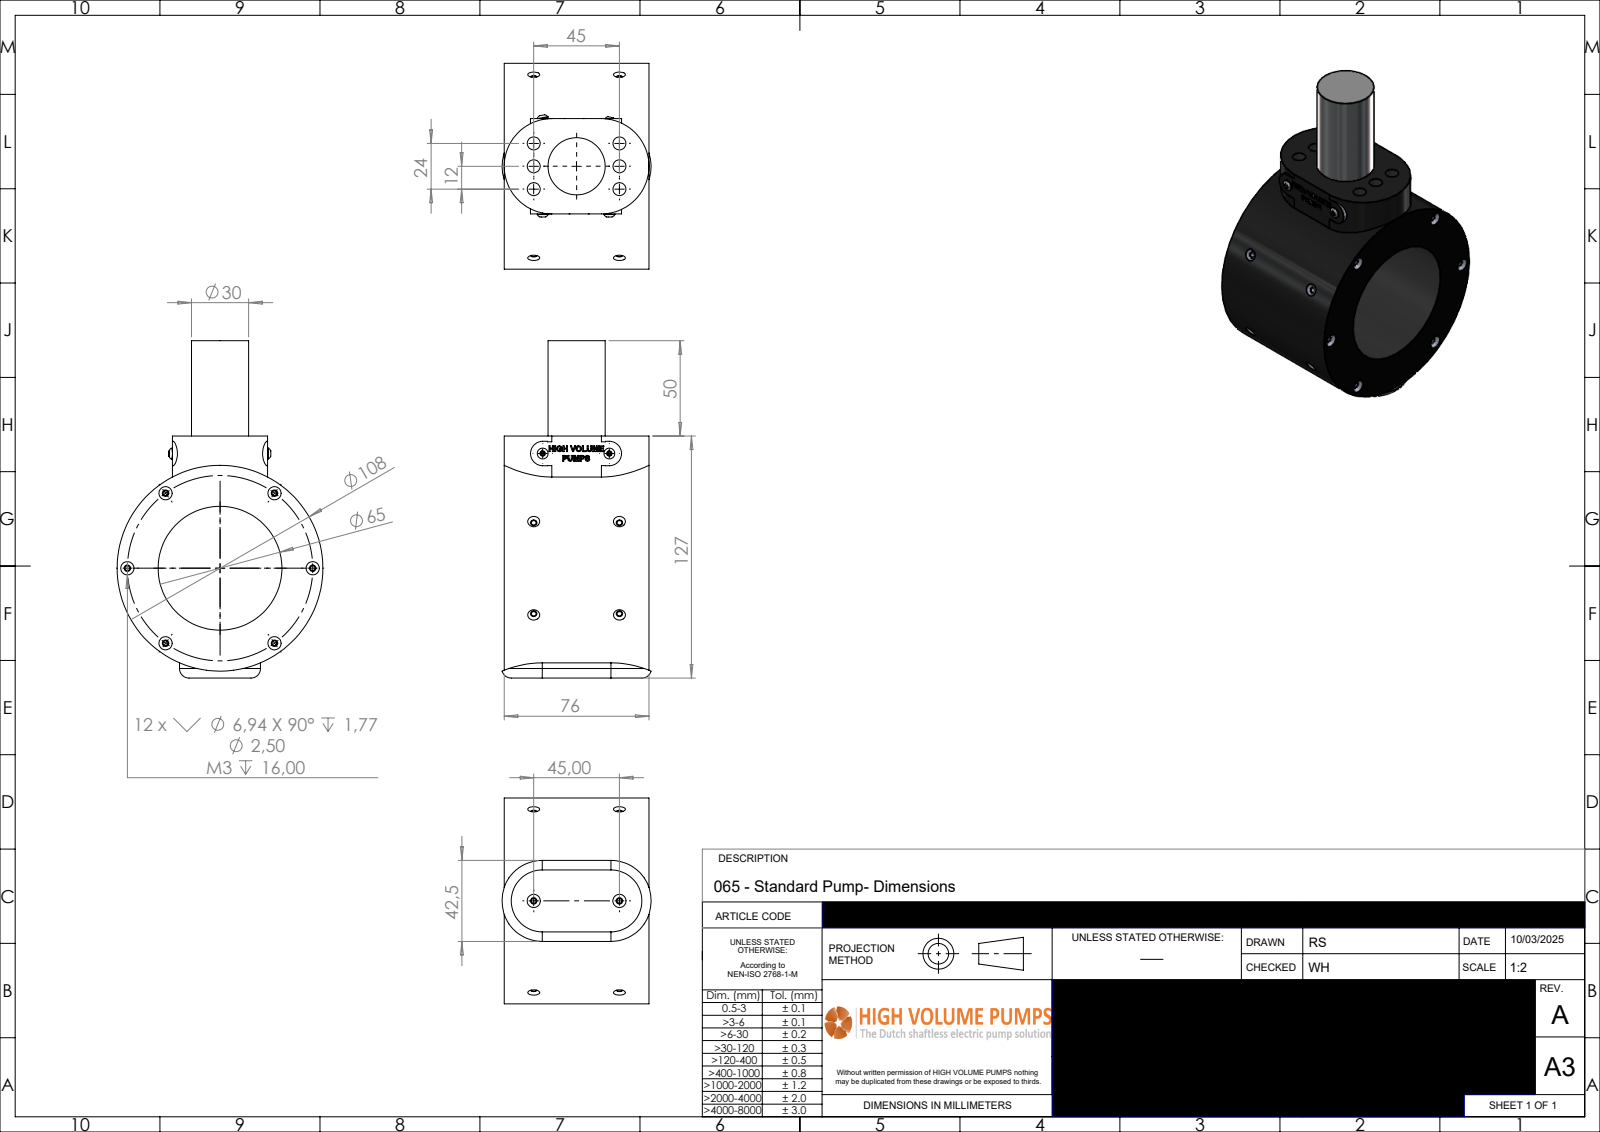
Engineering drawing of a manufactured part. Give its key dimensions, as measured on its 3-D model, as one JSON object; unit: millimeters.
{"part_name": "P-065-030-rev-A-SP", "step_written_by": "SolidWorks 2024 (AUTOMOTIVE_DESIGN)", "units": "millimeters", "bodies": {"solids": 1, "faces": 603, "planar": 375, "cylindrical": 51, "other": 177}, "overall_size": [177.01, 108, 78.22], "volume_mm3": 544639, "surface_area_mm2": 66474, "round_holes": [[2.5, 12], [6.8, 6], [65, 1], [108, 1]], "round_bosses_or_shafts": [[5.7, 3], [30, 1]], "partial_cylinders_radius": [[5, 2], [6.4, 2], [21.25, 2], [25, 2], [1.5, 1], [2.85, 1]], "face_to_face_distances": [76, 127.01, 50, 177.01, 118.01, 9, 59, 3.75, 46.25, 49.9], "hole_center_spacings": [45, 48.65, 12, 46.57, 86.69, 24, 44.17, 51]}
